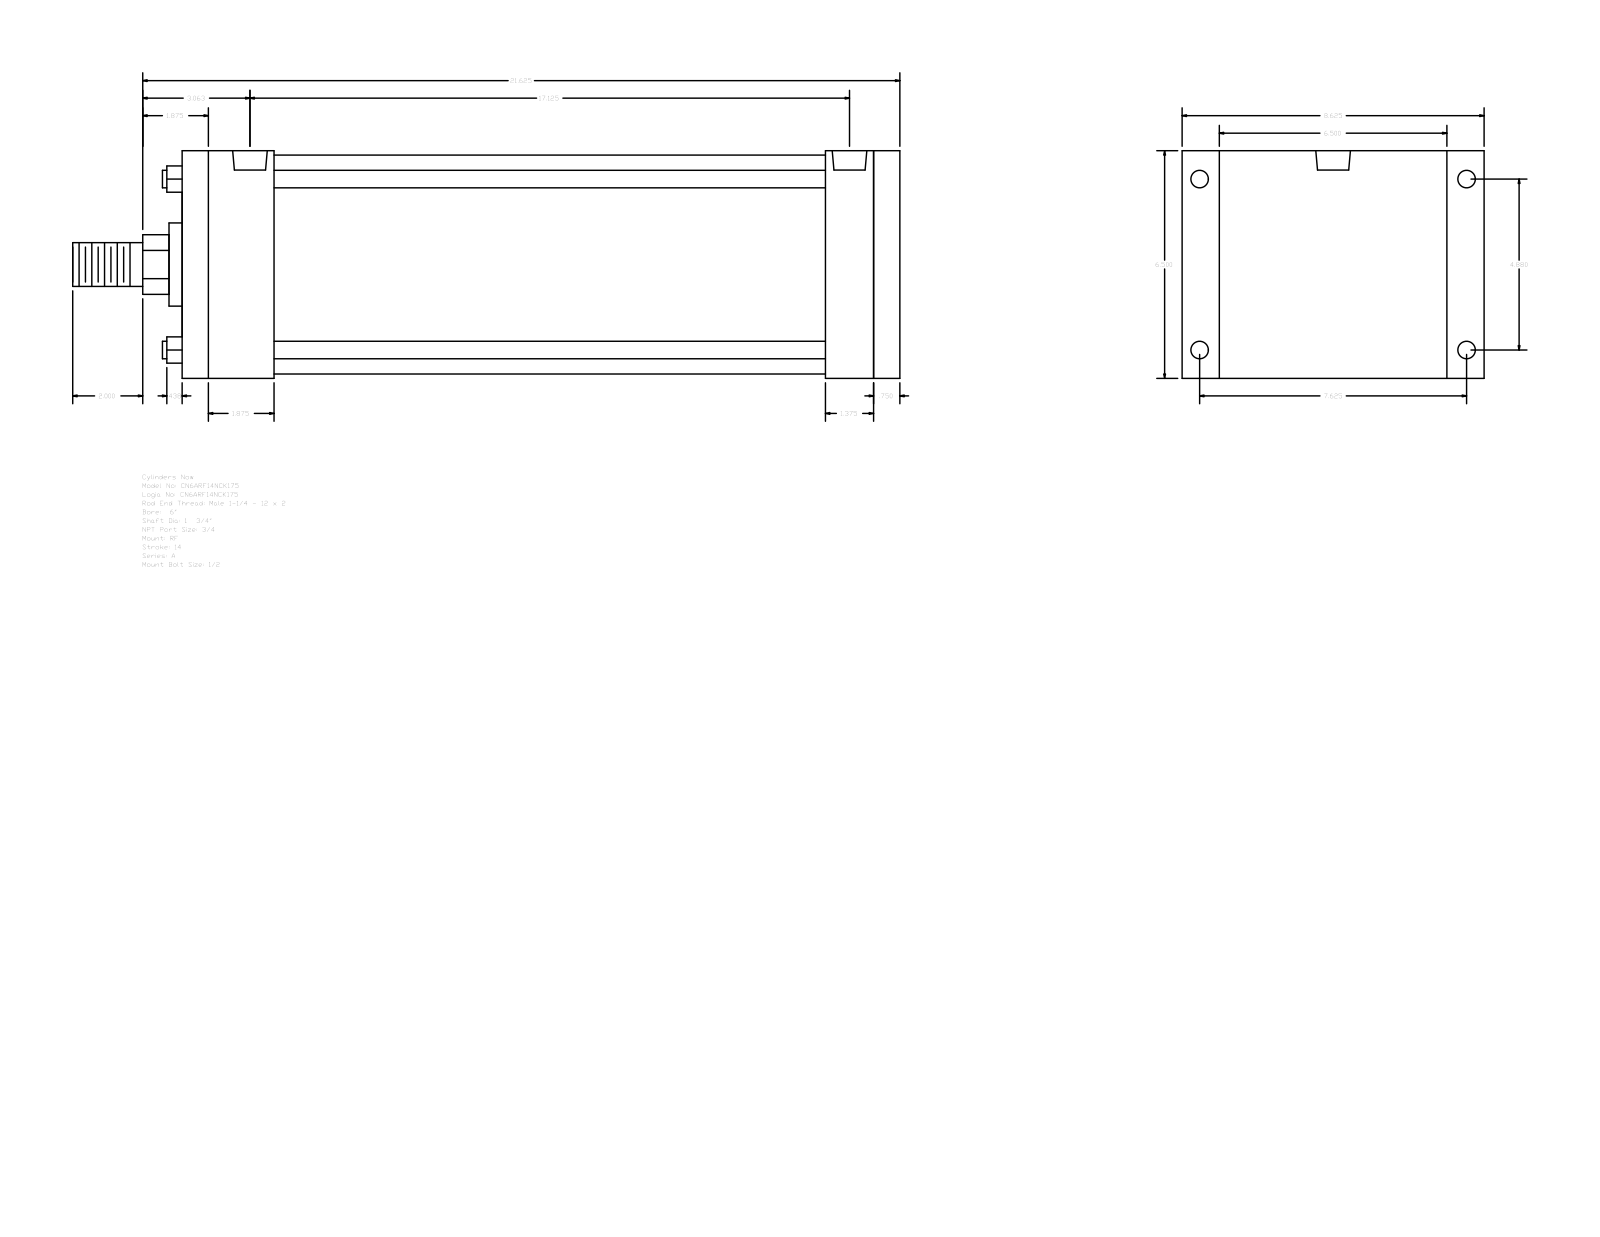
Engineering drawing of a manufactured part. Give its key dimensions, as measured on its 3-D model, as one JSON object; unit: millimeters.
{"part_name": "A_RF__0600_1.75", "step_written_by": "GSSL Pune (CONFIG_CONTROL_DESIGN)", "units": "millimeters", "bodies": {"solids": 0, "faces": 92, "planar": 64, "cylindrical": 28, "other": 0}, "overall_size": [600.08, 219.07, 165.1], "round_holes": [[12.7, 4], [15.08, 4], [25.12, 2]], "round_bosses_or_shafts": [[12.7, 4], [158.75, 1], [60.33, 1], [44.45, 1], [31.75, 1]], "partial_cylinders_radius": [[21.63, 1]], "face_to_face_distances": [165.1, 520.7, 501.66, 19.04, 66.68, 434.98, 454.02, 466.73, 400.05, 34.93], "hole_center_spacings": [5.56, 123.96, 193.68, 229.95, 423.85, 429.41, 434.97]}
